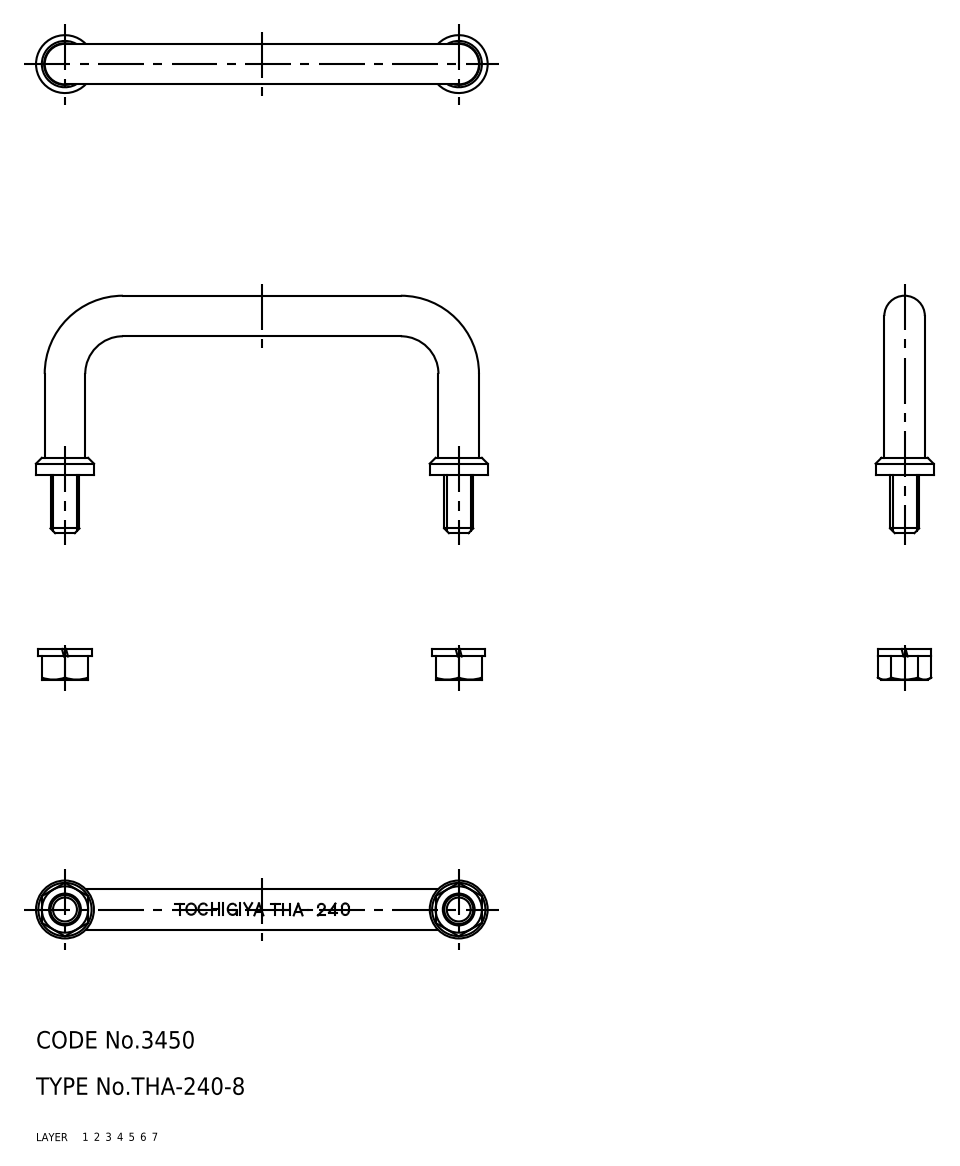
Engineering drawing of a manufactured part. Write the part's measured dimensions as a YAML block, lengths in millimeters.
part_name: "THA_240_8; pull; facing ring; nut (+1 more)"
step_written_by: "SolidWorks 2015 (AUTOMOTIVE_DESIGN)"
units: millimeters
bodies: {solids: 7, faces: 90, planar: 30, cylindrical: 34, other: 26}
overall_size: [78, 41, 10]
volume: 5388
surface_area: 4160
round_holes:
  - {diameter: 5, count: 2}
  - {diameter: 5.5, count: 2}
  - {diameter: 7.2, count: 2}
round_bosses_or_shafts:
  - {diameter: 7, count: 3}
  - {diameter: 10, count: 2}
  - {diameter: 9.2, count: 2}
face_to_face_distances: [8, 2, 3.3, 1.3, 3, 34, 4.3, 1, 4, 5.3]
hole_center_spacings: [68]
